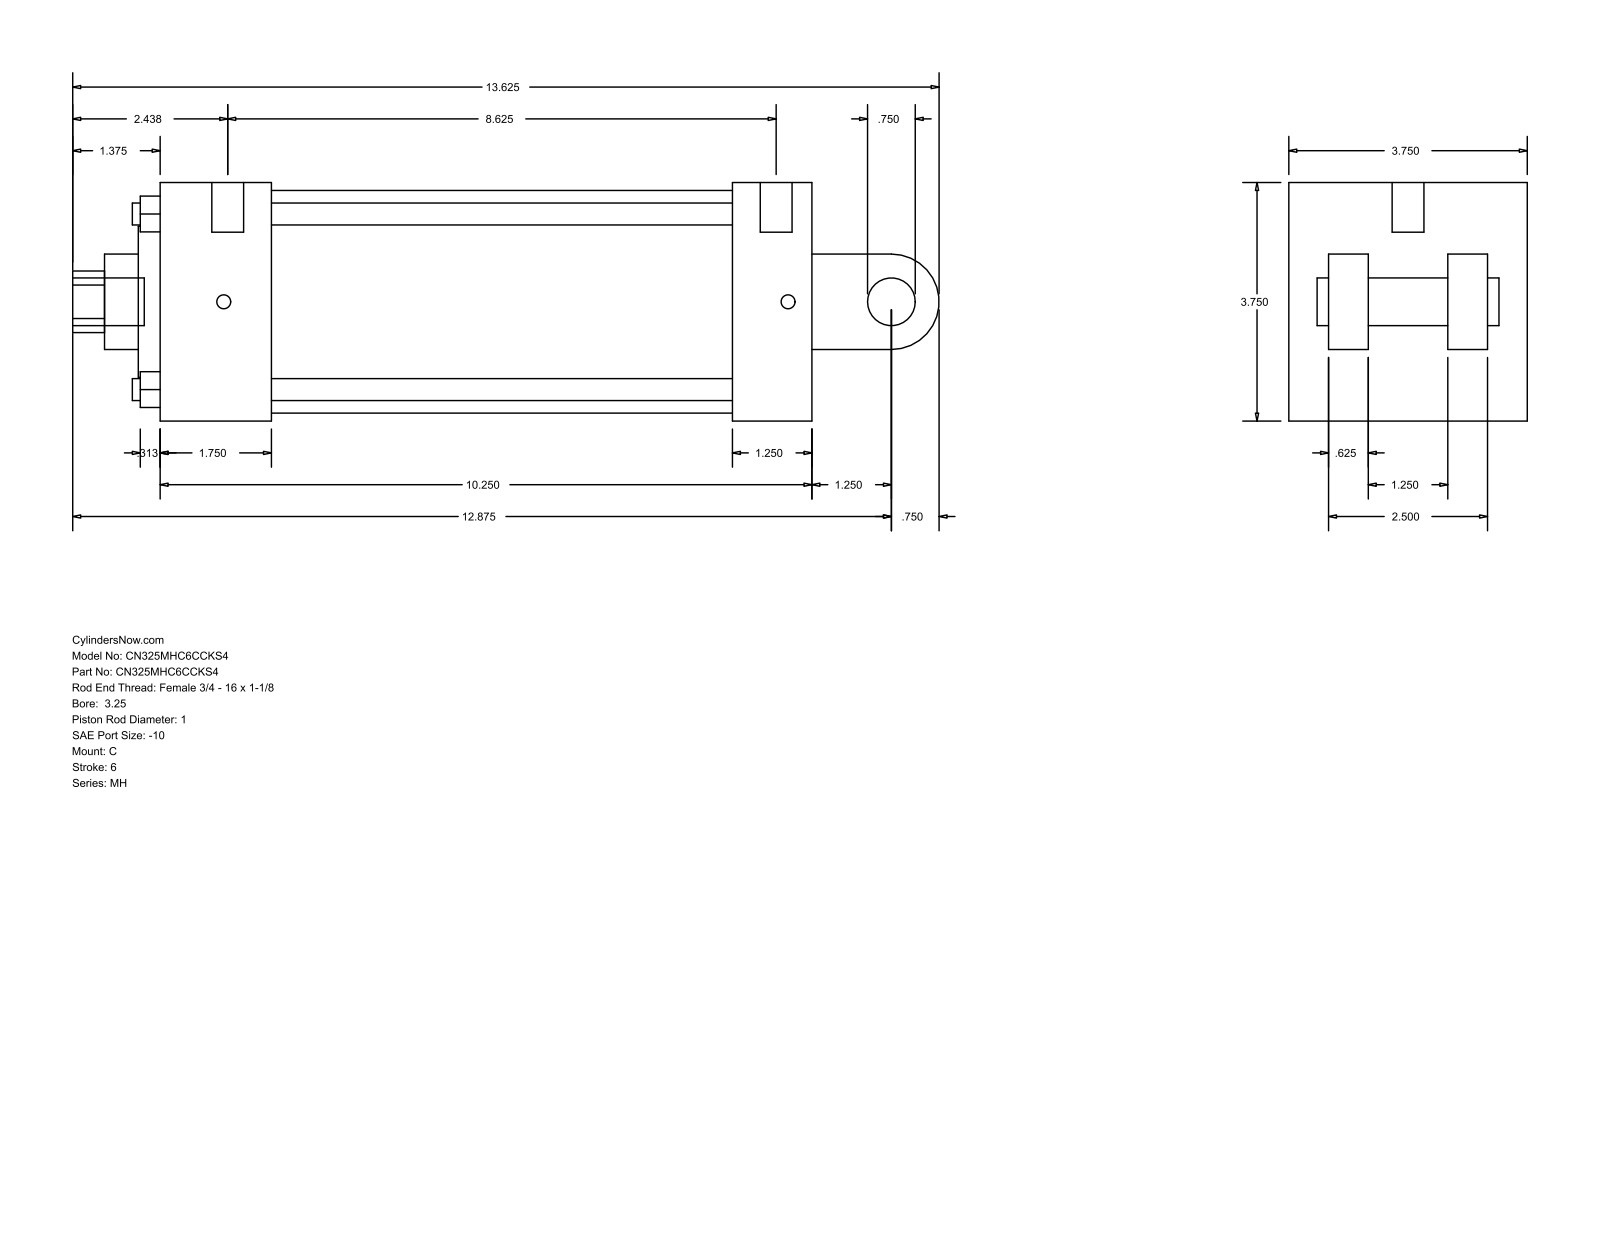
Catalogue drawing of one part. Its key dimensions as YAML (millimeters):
part_name: "MH_C__0325_1"
step_written_by: "GSSL Pune (CONFIG_CONTROL_DESIGN)"
units: millimeters
bodies: {solids: 0, faces: 101, planar: 71, cylindrical: 30, other: 0}
overall_size: [346.07, 95.25, 95.25]
round_holes:
  - {diameter: 8.76, count: 4}
  - {diameter: 5.56, count: 2}
  - {diameter: 12.7, count: 1}
  - {diameter: 25.4, count: 1}
  - {diameter: 38.1, count: 1}
  - {diameter: 60.33, count: 1}
  - {diameter: 88.9, count: 1}
round_bosses_or_shafts:
  - {diameter: 19.05, count: 2}
  - {diameter: 5.56, count: 2}
  - {diameter: 12.7, count: 1}
partial_cylinders:
  - {radius: 12.29, count: 1}
  - {radius: 19.05, count: 1}
face_to_face_distances: [95.24, 15.87, 260.35, 63.5, 79.37, 31.74, 47.63, 44.46, 228.6, 184.14]
hole_center_spacings: [49.57, 70.1, 99.14, 4.76]
